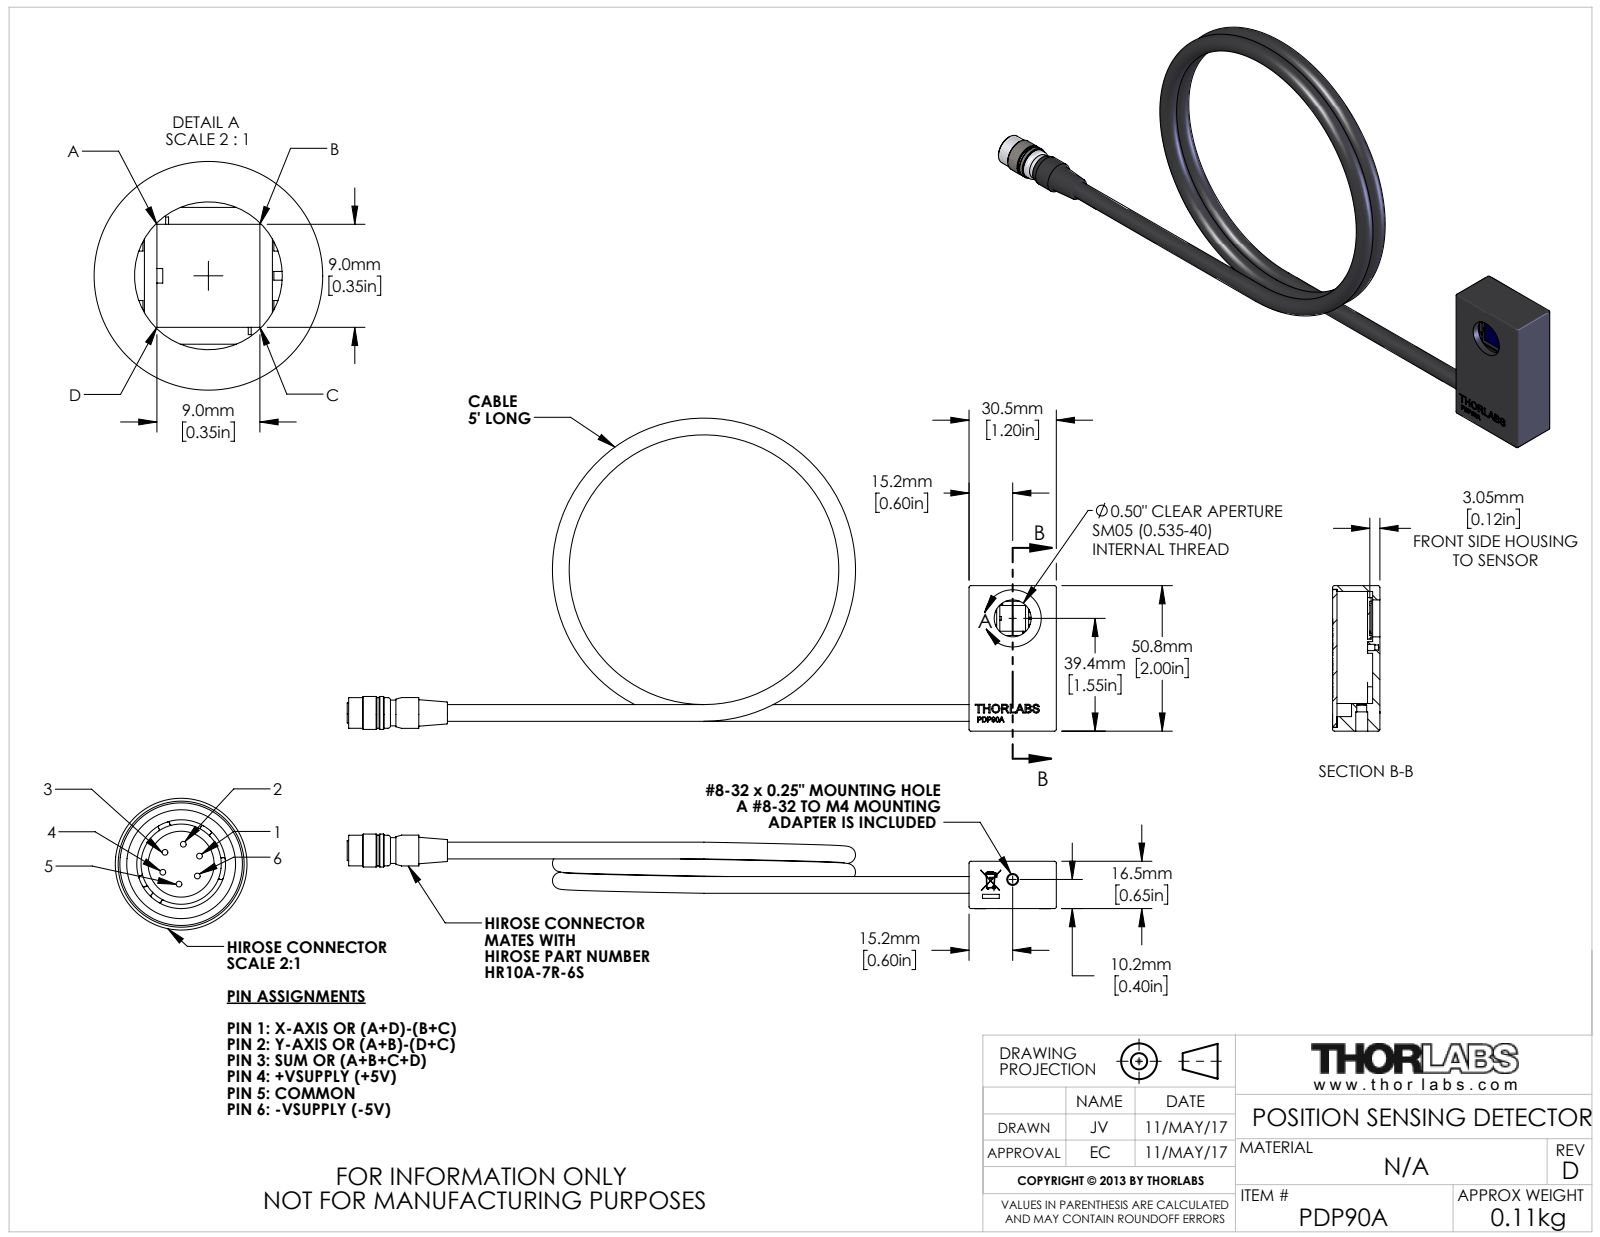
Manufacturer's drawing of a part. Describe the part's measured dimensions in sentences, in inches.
The part is named "17149-E0W". Its 3-D file was written by "SolidWorks 2016 (AUTOMOTIVE_DESIGN)". It is 7 solids with 2793 faces: 1827 planar, 225 cylindrical and 741 other. Overall it measures 9.75 by 4.302 by 1.025 inches. Its volume is 2.198 cubic inches and its surface area 44.94 square inches. Round holes: 10 of diameter 0.04, 5 of diameter 0.086, 4 of diameter 0.07, 4 of diameter 0.15, 2 of diameter 0.096, 1 of diameter 0.017, 1 of diameter 0.05, 1 of diameter 0.136, 1 of diameter 0.164, 1 of diameter 0.22, 1 of diameter 0.226, 1 of diameter 0.236. Round bosses or shafts: 6 of diameter 0.02, 2 of diameter 0.23, 2 of diameter 0.147, 1 of diameter 0.453, 1 of diameter 0.423, 1 of diameter 0.421, 1 of diameter 0.354, 1 of diameter 0.305. Partial cylindrical surfaces (rounded edges, fillets, slot ends): 12 of radius 0.025, 12 of radius 0.063, 10 of radius 0.004, 10 of radius 0.006, 10 of radius 0.02, 8 of radius 0.04, 4 of radius 0.031, 3 of radius 0.01. The main face-to-face distances are 0.65, 0.06, 0.59, 0.08, 0.1, 0.55, 0.49, 1.12, 1.2, 1.04. The hole center spacings are 0.1, 0.288, 0.426, 0.2, 0.23, 0.3, 0.414, 0.46.
